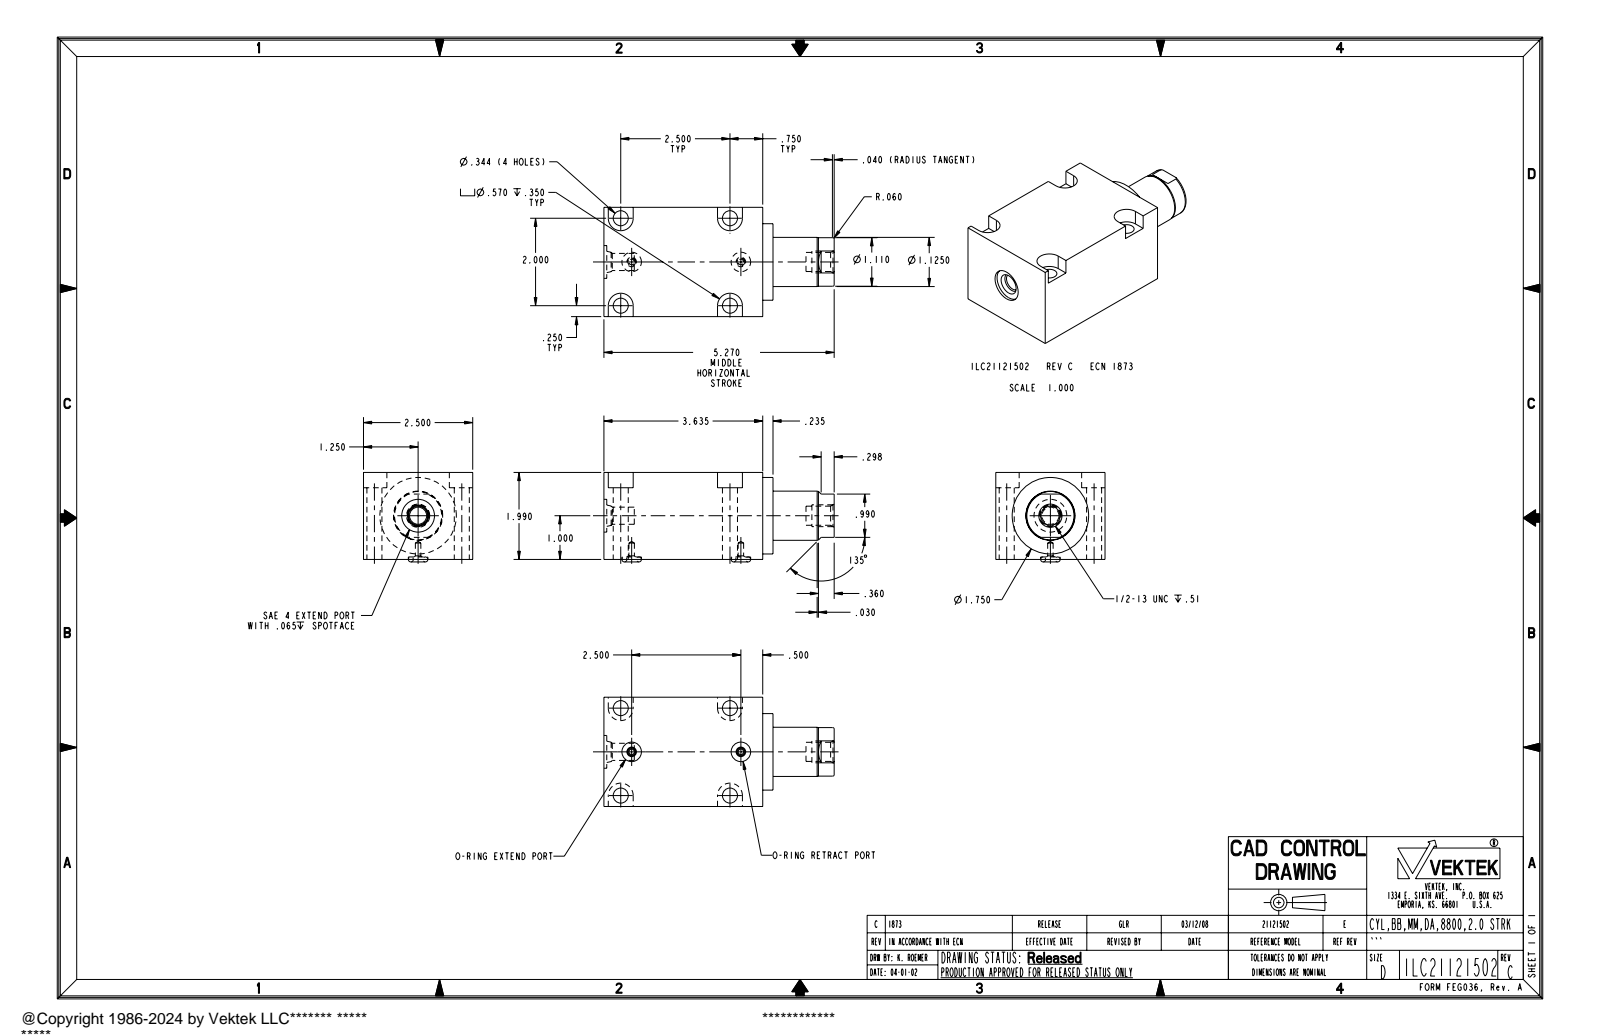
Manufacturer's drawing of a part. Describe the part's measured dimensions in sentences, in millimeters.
The part is named "ILC21121502". Its 3-D file was written by "PRO/ENGINEER BY PARAMETRIC TECHNOLOGY CORPORATION, 2007460 (AUTOMOTIVE_DESIGN_CC2)". It is 1 solid with 90 faces: 30 planar, 34 cylindrical and 26 other. Overall it measures 133.9 by 63.5 by 52 millimeters. Its volume is 308 400 cubic millimeters and its surface area 38 670 square millimeters. Round holes: 4 of diameter 8.7, 2 of diameter 3.2, 2 of diameter 11.4, 1 of diameter 10, 1 of diameter 11.1, 1 of diameter 19.1. Round bosses or shafts: 1 of diameter 44.5, 1 of diameter 28.6, 1 of diameter 28.2, 1 of diameter 12.7. Partial cylindrical surfaces (rounded edges, fillets, slot ends): 4 of radius 7.2. The main face-to-face distances are 50.5, 63.5, 92.3, 6, 98.3, 41.7, 8.9, 35.6, 41.5, 133.9. The hole center spacings are 26.2, 63.5, 50.8, 62.5, 74.3, 81.3.
